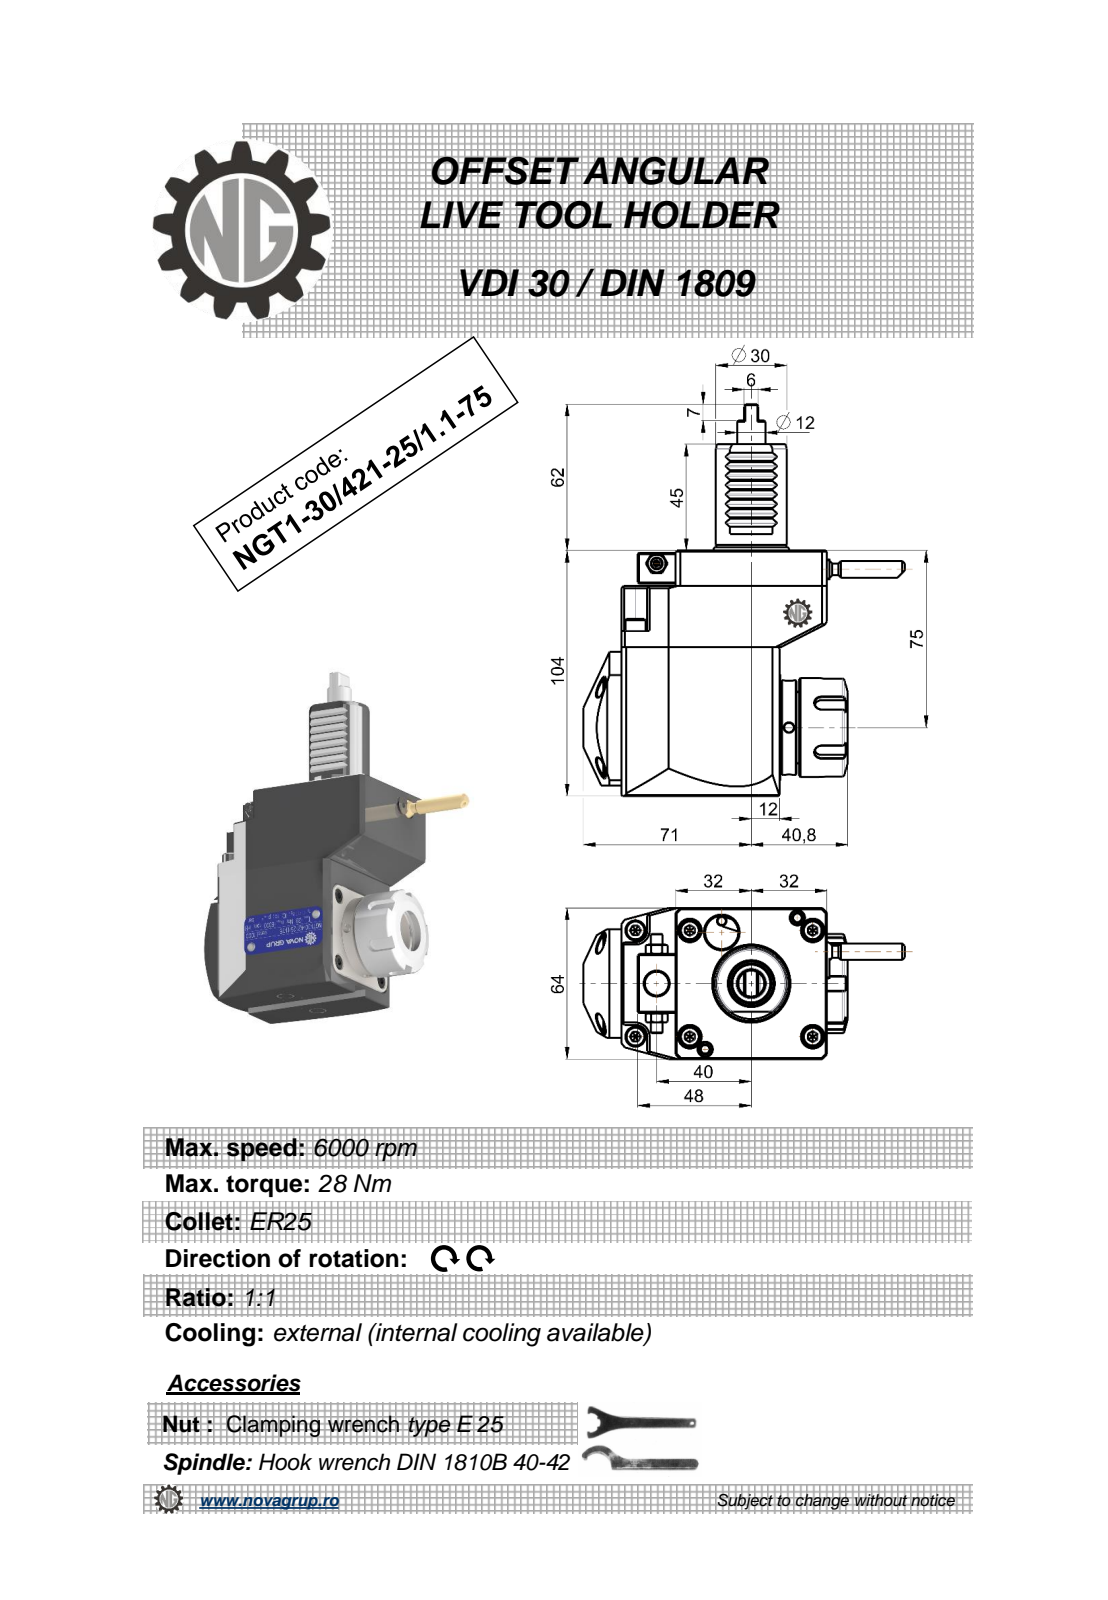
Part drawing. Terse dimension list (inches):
name: NGT1_30_421_25_1_1_75
written by: PRO/ENGINEER BY PARAMETRIC TECHNOLOGY CORPORATION, 2010280 (CONFIG_CONTROL_DESIGN)
unit: in
bodies: 1 solid, 434 faces (203 planar, 88 cylindrical, 143 other)
size: 6.535 × 5.35 × 2.575
volume: 33.81 in³; area: 82.15 in²
holes: 2× ⌀0.157, 1× ⌀0.098, 1× ⌀0.118, 1× ⌀0.165, 1× ⌀0.374, 1× ⌀0.394, 1× ⌀0.799
bosses: 2× ⌀0.353, 2× ⌀0.197, 1× ⌀1.654, 1× ⌀1.575, 1× ⌀1.299, 1× ⌀1.181, 1× ⌀0.472, 1× ⌀0.276
rounds: 12× R0.01, 8× R0.012, 5× R0.118, 4× R0.138, 2× R0.031, 1× R1.26
face distances: 2.52, 4.094, 3.425, 2.646, 0.78, 0.787, 0.591, 3.504, 2.638, 0.276
hole spacings: 0.533, 2.203, 2.677, 2.691, 3.513
